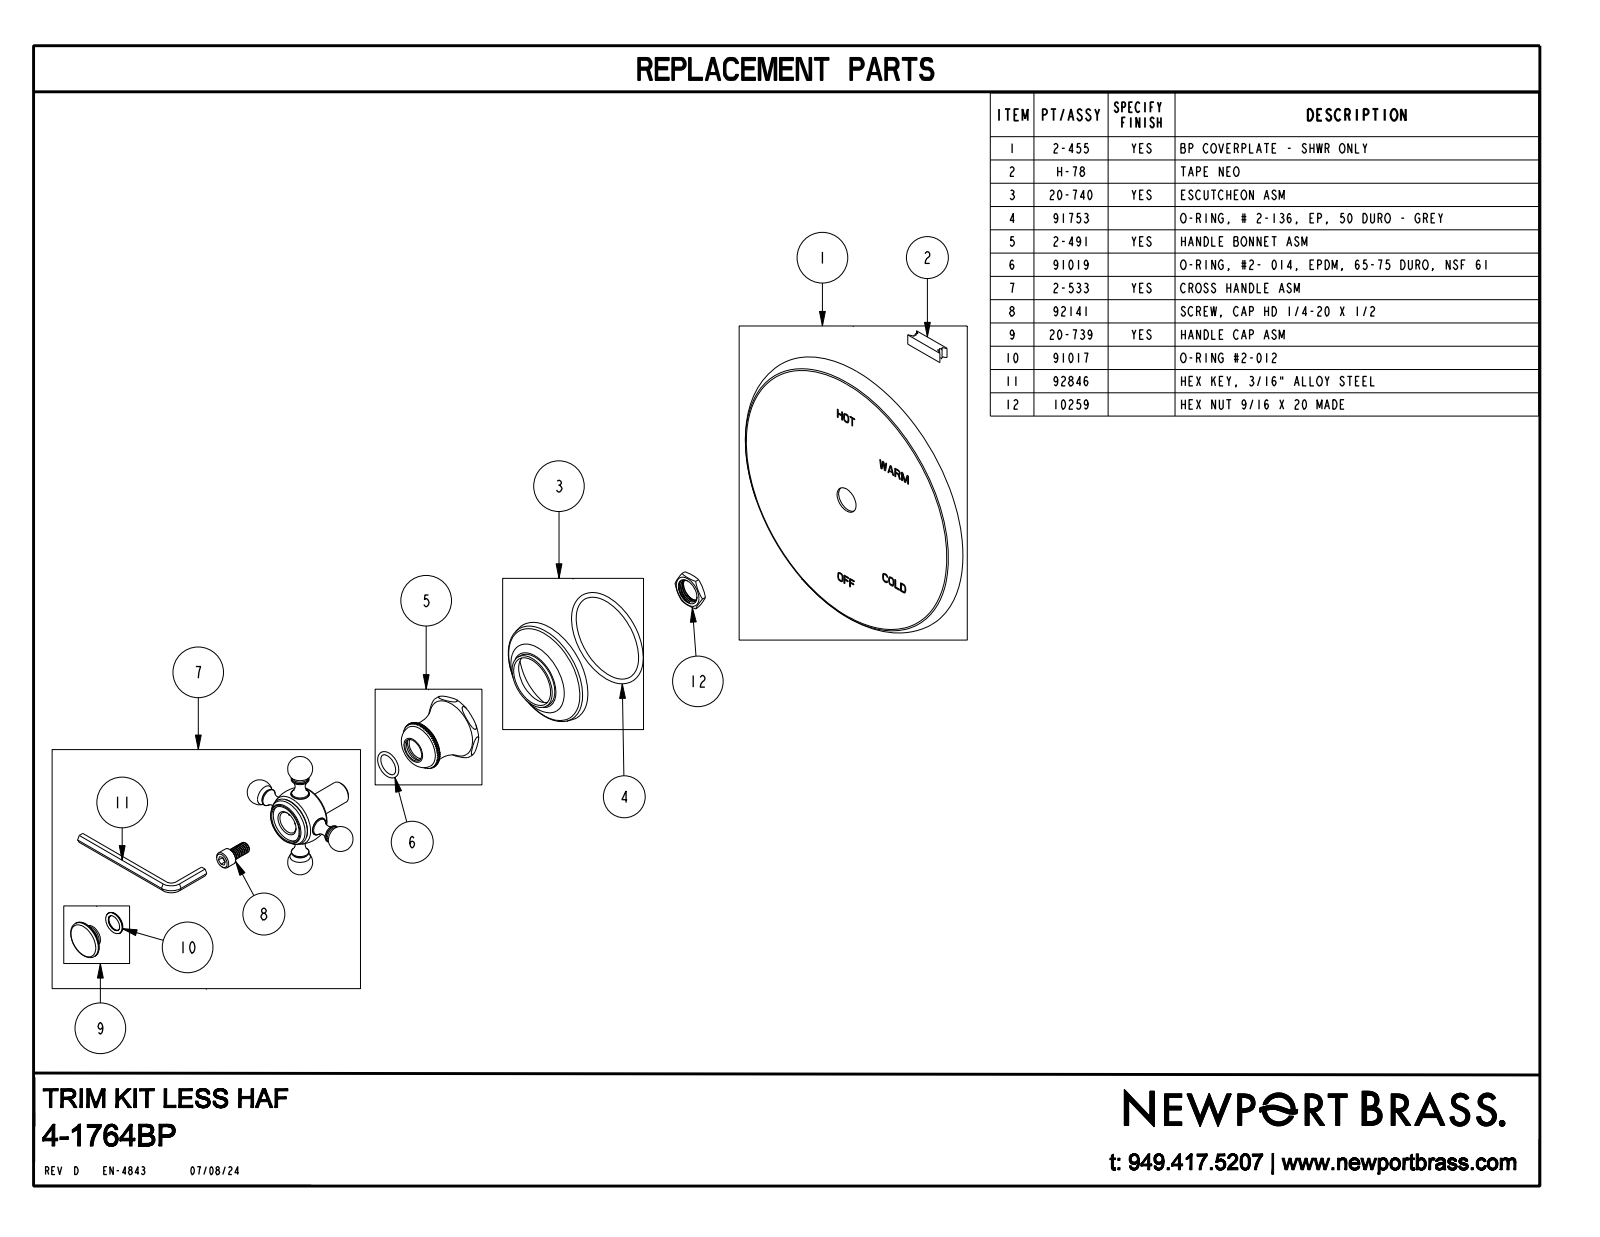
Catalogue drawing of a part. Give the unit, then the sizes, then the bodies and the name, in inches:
Units: inches
Overall size (bounding box): 6.625 × 6.625 × 3.66
Round holes (diameter × count): ⌀0.41 ×2, ⌀0.855 ×1
Round bosses / shafts (diameter × count): ⌀0.392 ×2, ⌀0.84 ×1, ⌀0.5 ×1
Main face-to-face distances: 0.313, 2.79, 2.477, 1.375, 0.293, 0.02, 2.497, 3.5, 3.207, 3.187
Volume: 14.59 in³ · Surface area: 90.03 in²
Bodies: 1 solid, 600 faces (488 planar, 22 cylindrical, 90 other)
Part name (STEP PRODUCT): 4-1764BP
STEP written by: CREO PARAMETRIC BY PTC INC, 2018400 (CONFIG_CONTROL_DESIGN)
